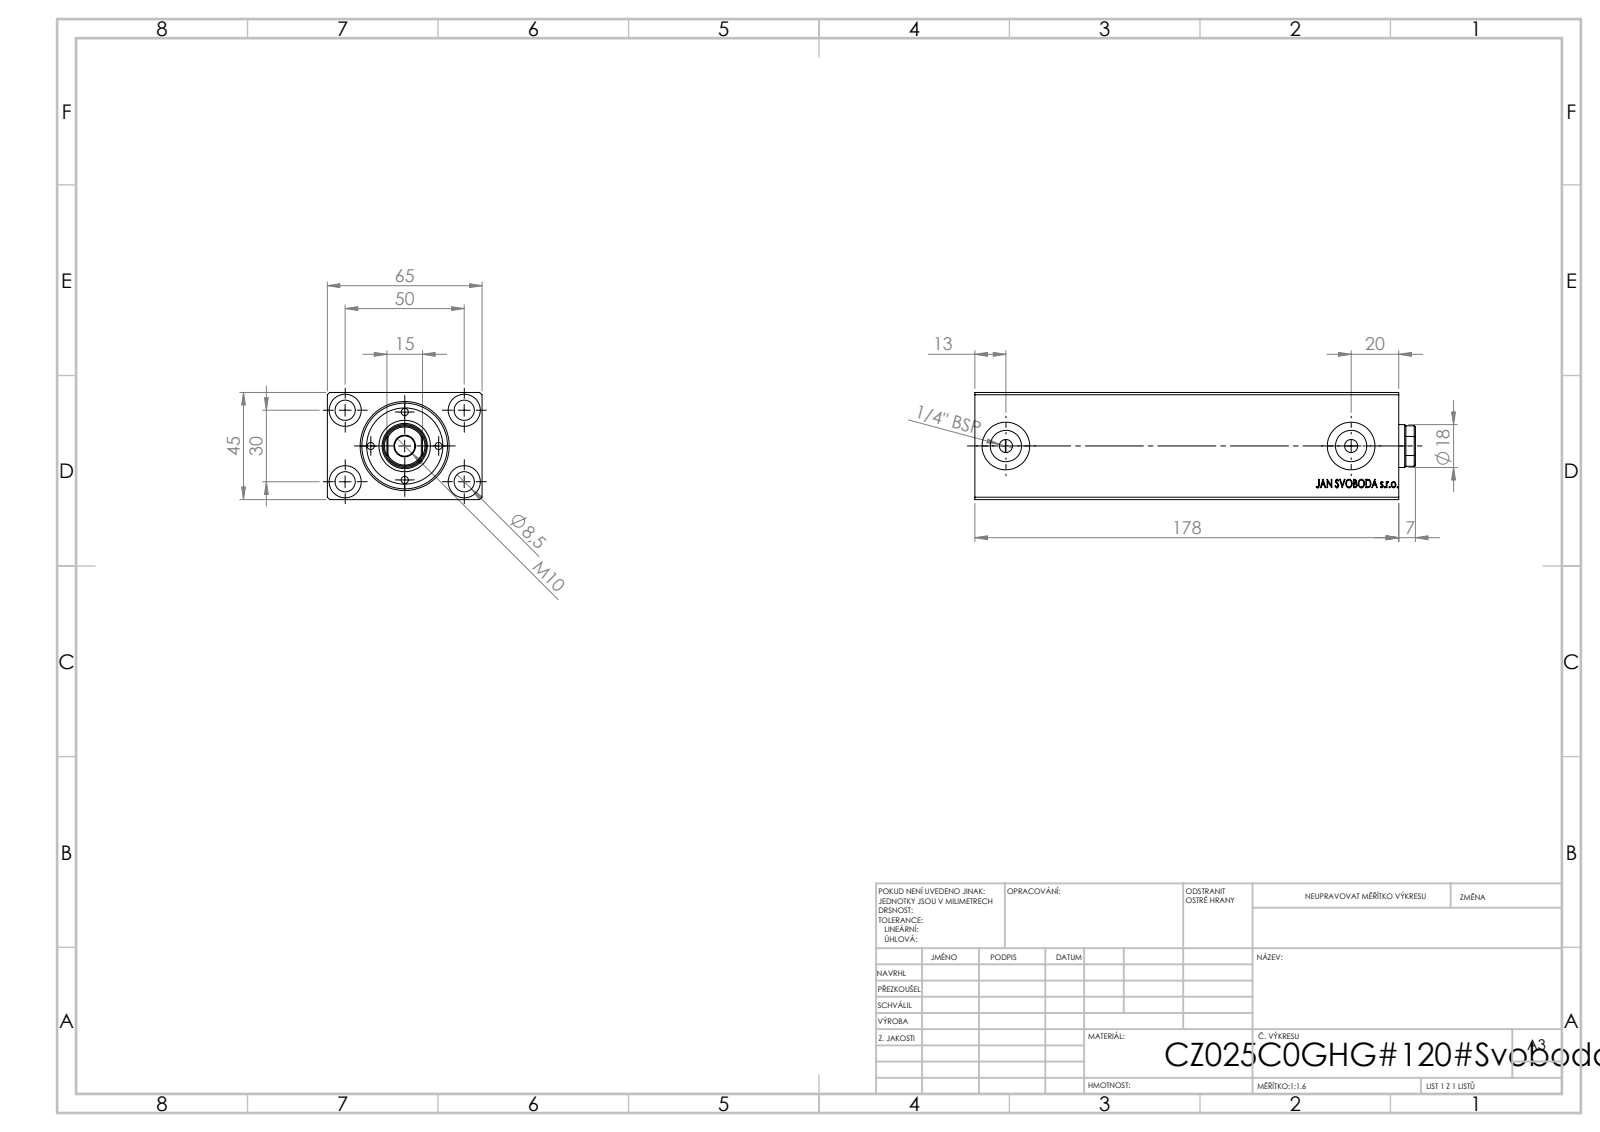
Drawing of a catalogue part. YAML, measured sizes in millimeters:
step_written_by: "SolidWorks 2019 (CONFIG_CONTROL_DESIGN)"
units: millimeters
bodies: {solids: 1, faces: 824, planar: 396, cylindrical: 46, other: 382}
overall_size: [178, 65, 45]
volume: 383615
surface_area: 79091
round_holes:
  - {diameter: 8.5, count: 4}
  - {diameter: 13.5, count: 4}
  - {diameter: 5.5, count: 2}
  - {diameter: 8, count: 2}
  - {diameter: 13.16, count: 2}
  - {diameter: 20, count: 2}
  - {diameter: 25, count: 1}
  - {diameter: 36, count: 1}
face_to_face_distances: [45, 65, 178, 177.8, 10.33, 167.67, 7, 170.8, 171, 76.36]
hole_center_spacings: [29.15, 30, 50, 58.31, 125, 145]
